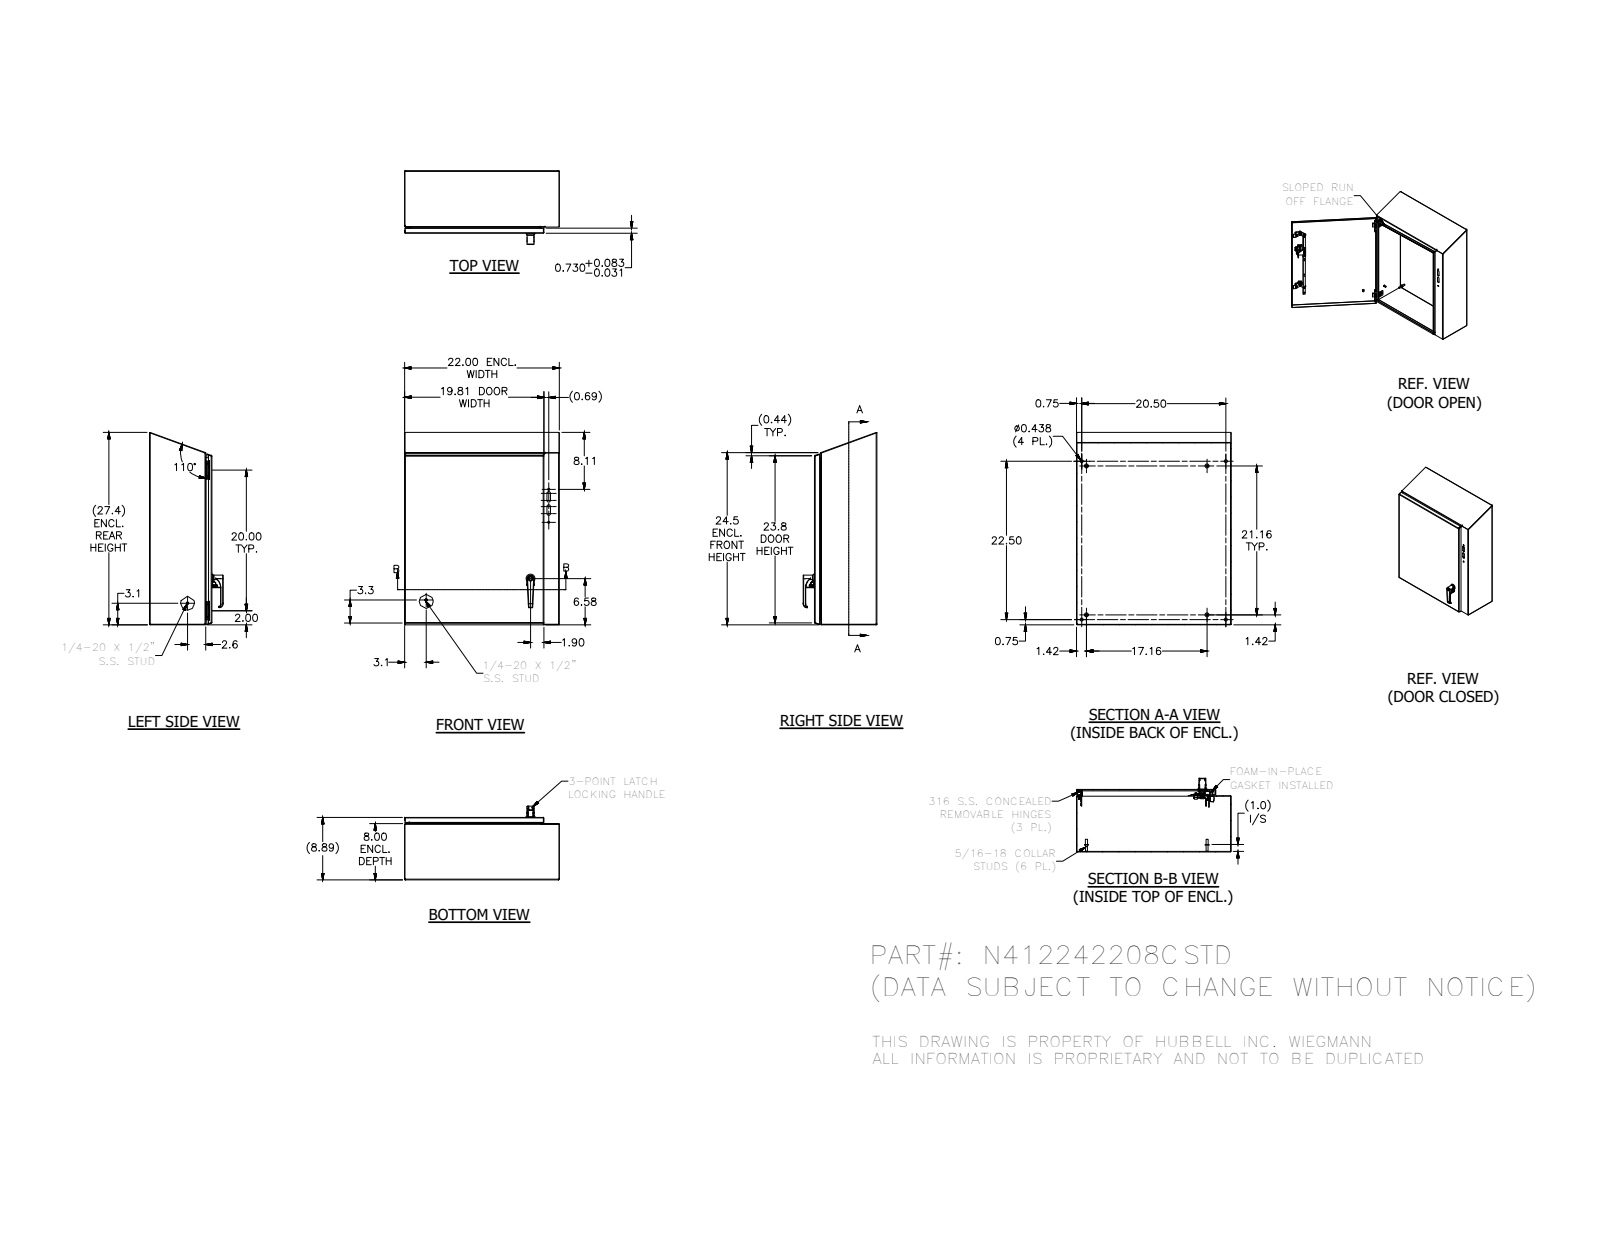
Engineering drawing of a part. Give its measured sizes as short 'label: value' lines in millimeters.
name: N412242208CSTD
written by: SolidWorks 2018 (AUTOMOTIVE_DESIGN)
unit: mm
bodies: 63 solids, 2119 faces (839 planar, 751 cylindrical, 529 other)
size: 695.1 × 558.8 × 266.2
volume: 2 637 000 mm³; area: 2 780 000 mm²
holes: 6× ⌀3.7, 5× ⌀4, 4× ⌀2.4, 4× ⌀3.9, 4× ⌀4.2, 4× ⌀4.4, 4× ⌀4.7, 4× ⌀11.1, 3× ⌀8.1, 2× ⌀5, 2× ⌀5.4, 2× ⌀5.6
bosses: 12× ⌀6.4, 8× ⌀7.6, 4× ⌀14.3, 4× ⌀11.1, 4× ⌀9.1, 4× ⌀8.1, 4× ⌀6.5, 4× ⌀4.8
rounds: 38× R0.5, 30× R0.3, 29× R0.8, 26× R1.3, 25× R3.2, 19× R2.7, 18× R0.4, 16× R0.6
face distances: 1.9, 223.9, 222, 225.7, 556.9, 201.3, 22.5, 555, 558.8, 20.7
hole spacings: 508, 12.7, 371.5, 530.1, 16.7, 16.8, 25, 33.2
